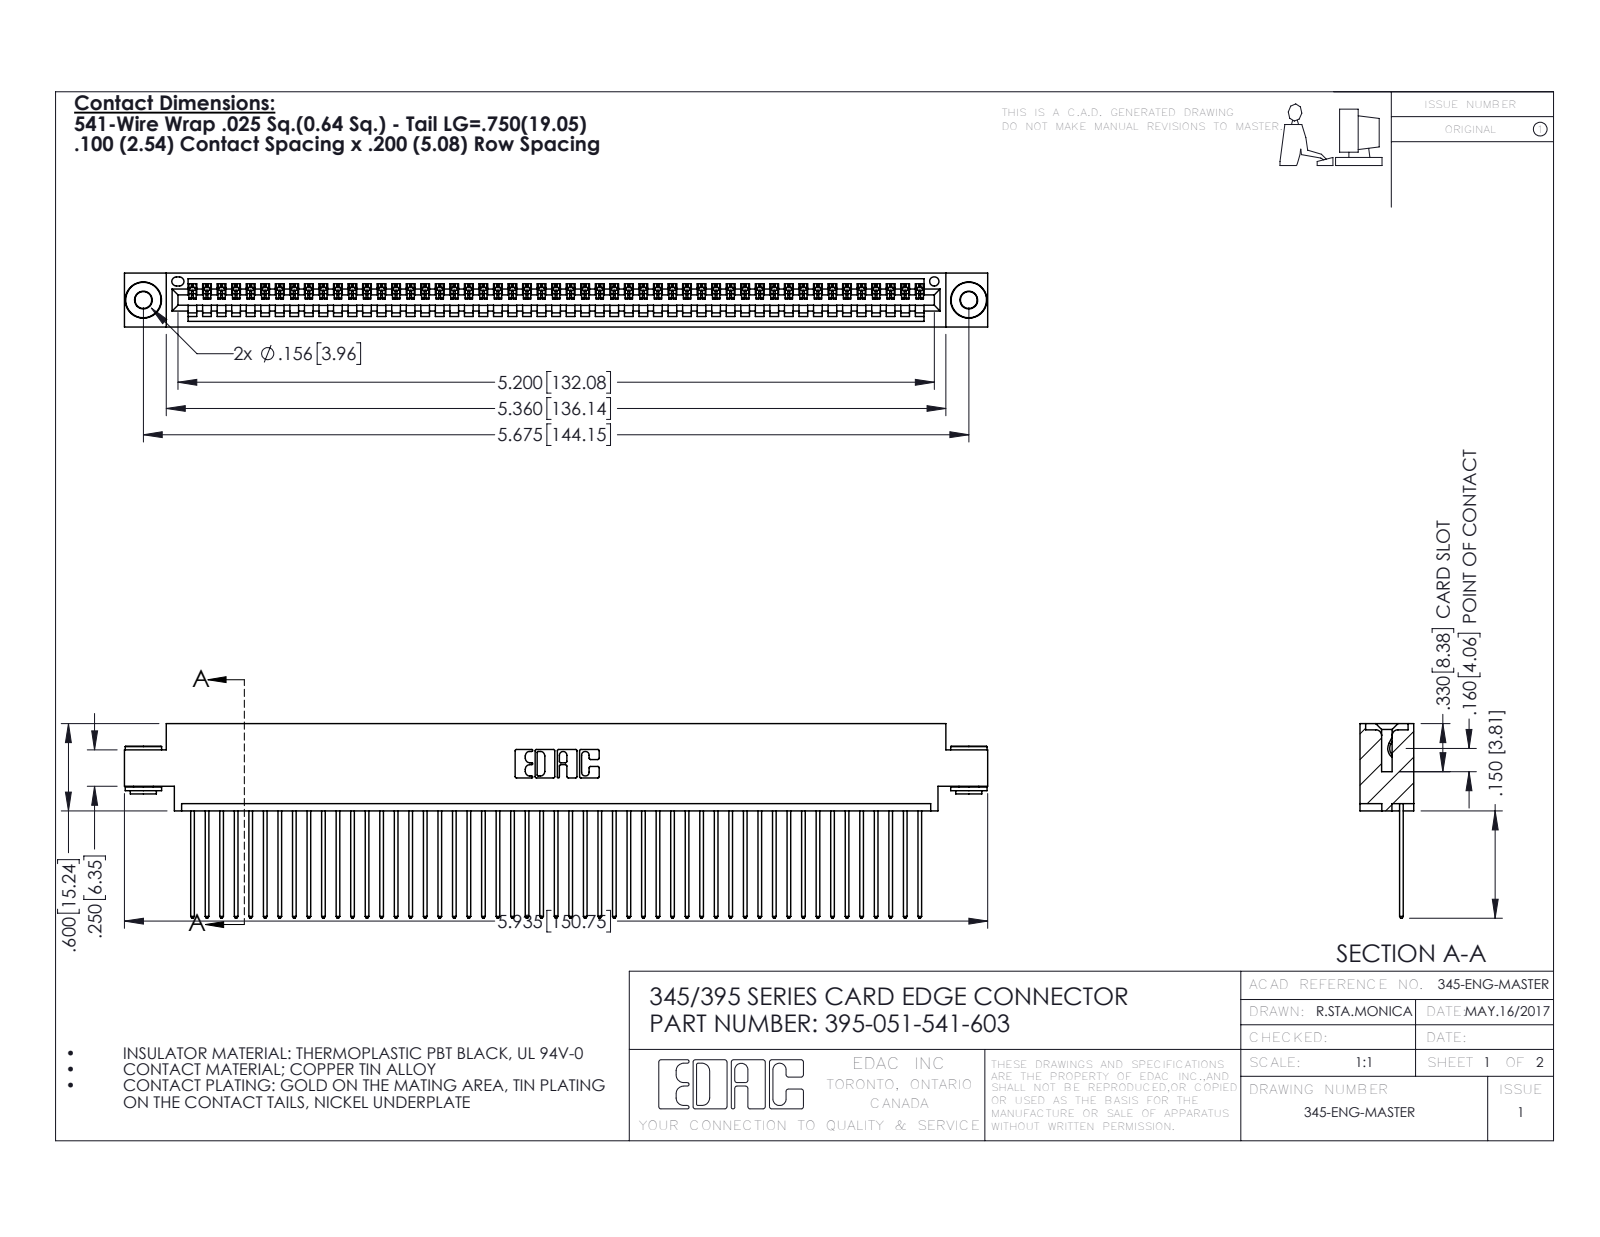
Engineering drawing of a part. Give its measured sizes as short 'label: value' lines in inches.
name: 345-250-002_345-250-002-102; 345-292-001_345-293-141; 395-051-541-603; 345 Part_0.170 Offset - 0.156 Dia-TH
written by: SolidWorks 2016 (CONFIG_CONTROL_DESIGN)
unit: in
bodies: 54 solids, 3126 faces (2134 planar, 984 cylindrical, 8 other)
size: 5.935 × 1.337 × 0.37
volume: 0.883 in³; area: 32.05 in²
holes: 2× ⌀0.116, 2× ⌀0.156, 1× ⌀0.064
bosses: 2× ⌀0.25, 2× ⌀0.18, 2× ⌀0.136
rounds: 102× R0.006, 102× R0.01, 22× R0.01, 6× R0.007, 6× R0.031, 3× R0.026, 2× R0.031, 2× R0.04
face distances: 0.072, 0.298, 0.37, 0.098, 0.272, 0.025, 0.2, 0.225, 0.175, 0.149
hole spacings: 0.27, 5.439, 5.675
